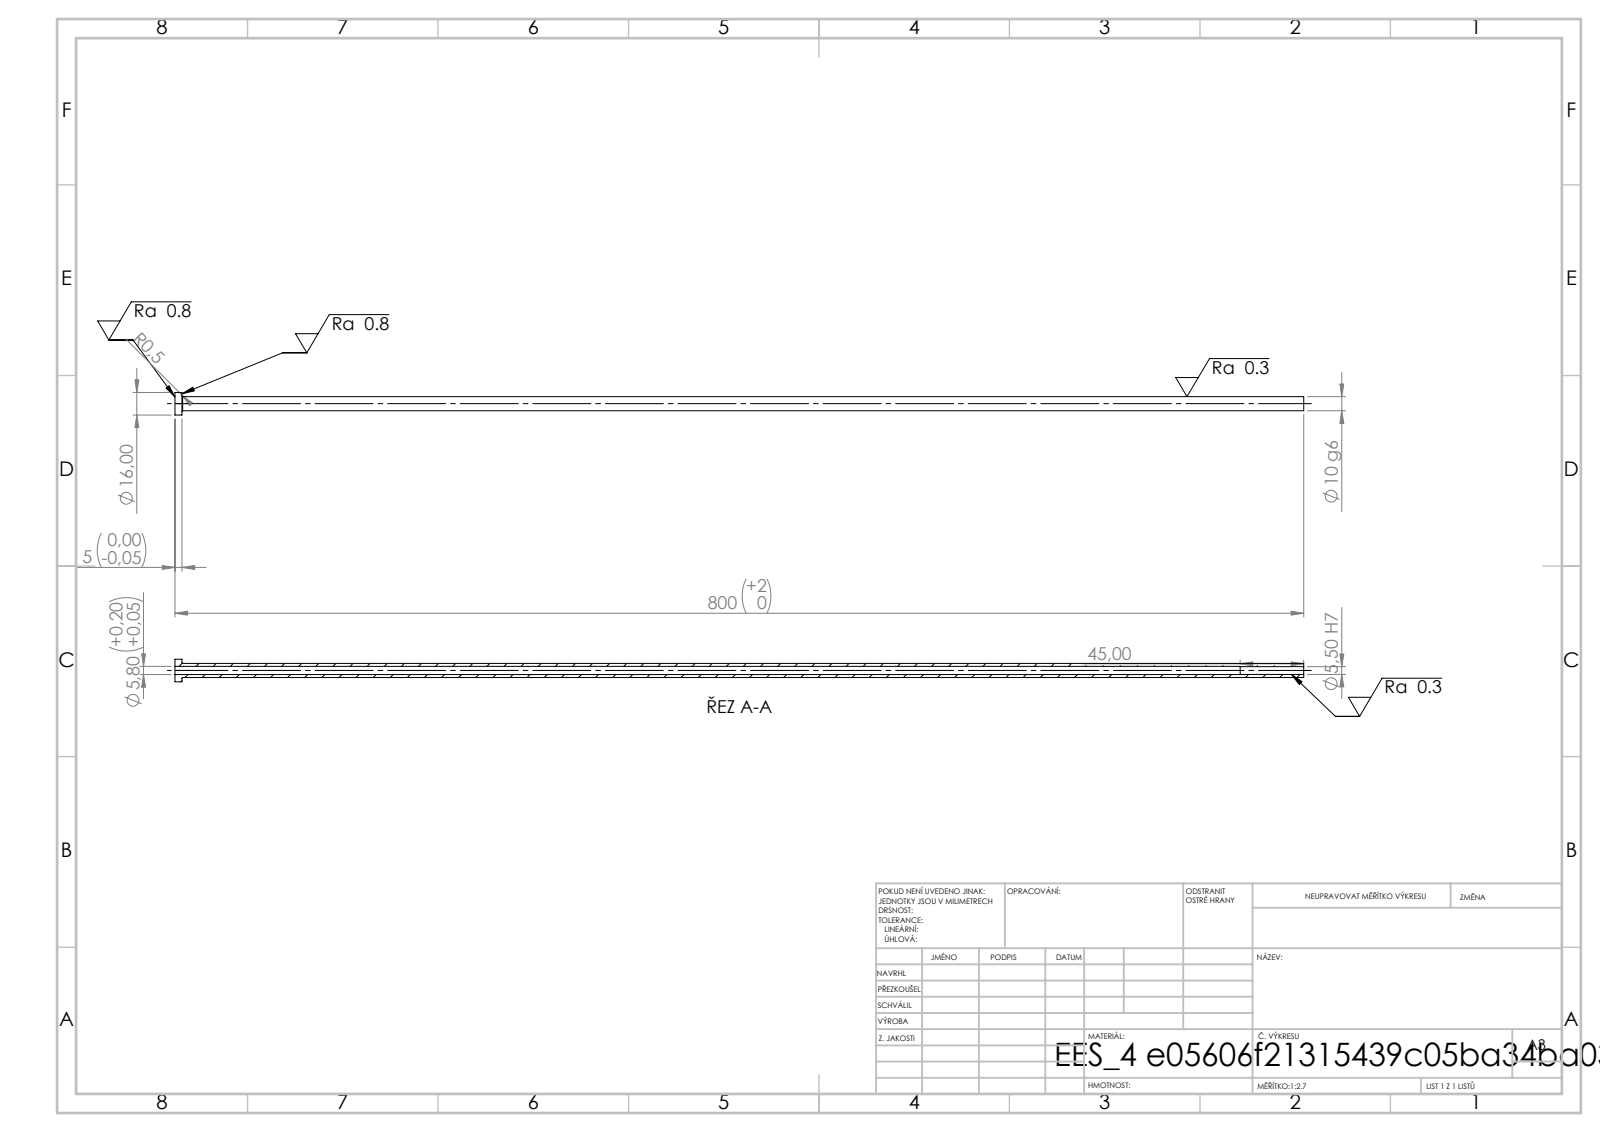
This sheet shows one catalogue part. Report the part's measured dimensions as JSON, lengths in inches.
{"step_written_by": "SolidWorks 2019 (CONFIG_CONTROL_DESIGN)", "units": "inches", "bodies": {"solids": 1, "faces": 14, "planar": 4, "cylindrical": 8, "other": 2}, "overall_size": [31.496, 0.63, 0.63], "volume_in3": 2.589, "surface_area_in2": 62.17, "round_holes": [[0.217, 1], [0.228, 1]], "round_bosses_or_shafts": [[0.63, 1], [0.394, 1]], "face_to_face_distances": [0.197, 31.496, 31.299, 29.724, 29.528, 1.772]}
